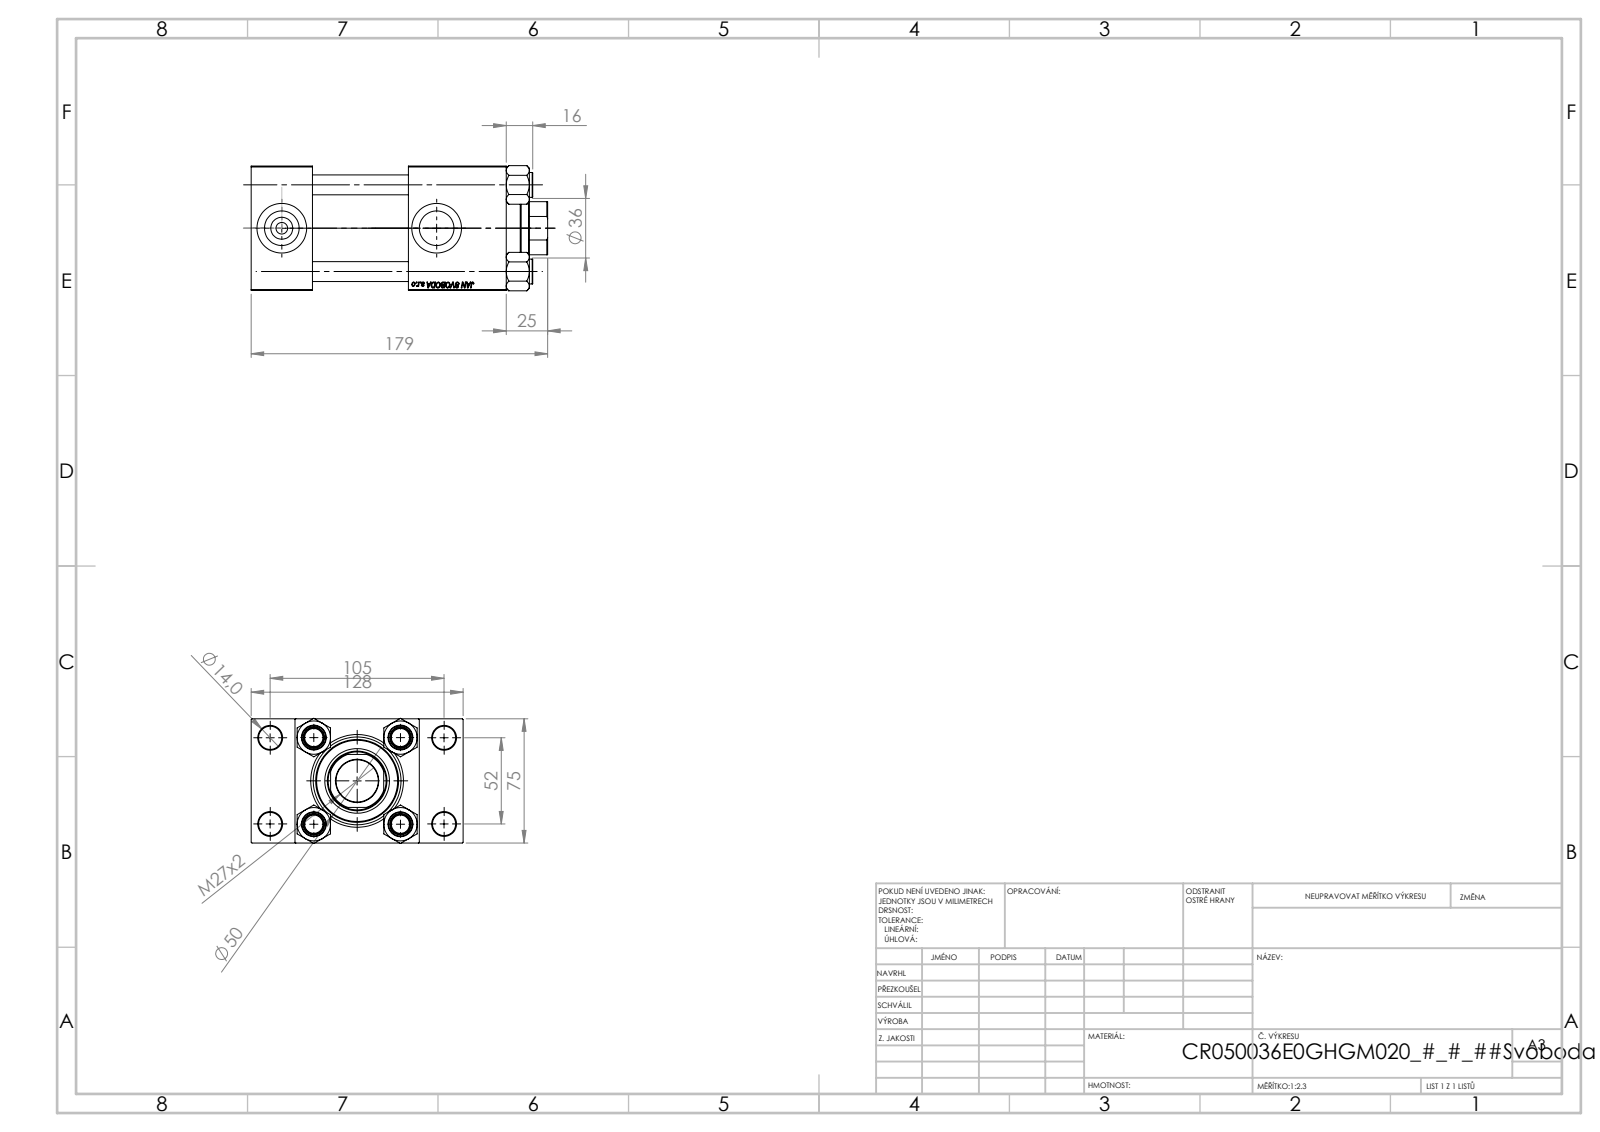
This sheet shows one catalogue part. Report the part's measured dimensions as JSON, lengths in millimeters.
{"part_name": "V215_VC_A; V215CR_VCP_E; V215CR_E_Body; V215CR_TYCINKA_E (+1 more)", "step_written_by": "SolidWorks 2019 (CONFIG_CONTROL_DESIGN)", "units": "millimeters", "bodies": {"solids": 11, "faces": 1136, "planar": 498, "cylindrical": 86, "other": 552}, "overall_size": [179, 128, 75.54], "volume_mm3": 817416, "surface_area_mm2": 181251, "round_holes": [[12, 4], [14, 4], [7, 2], [20.96, 2], [30, 2], [25.5, 1], [36, 1], [39, 1], [41, 1], [53, 1]], "round_bosses_or_shafts": [[15, 4], [56, 1], [50, 1]], "partial_cylinders_radius": [[17.5, 1]], "face_to_face_distances": [75, 37, 26.5, 101.5, 95, 154, 117, 58, 59, 125.3], "hole_center_spacings": [26.35, 36.98, 52.3, 58.43, 58.59, 78.65, 94.37, 52]}
